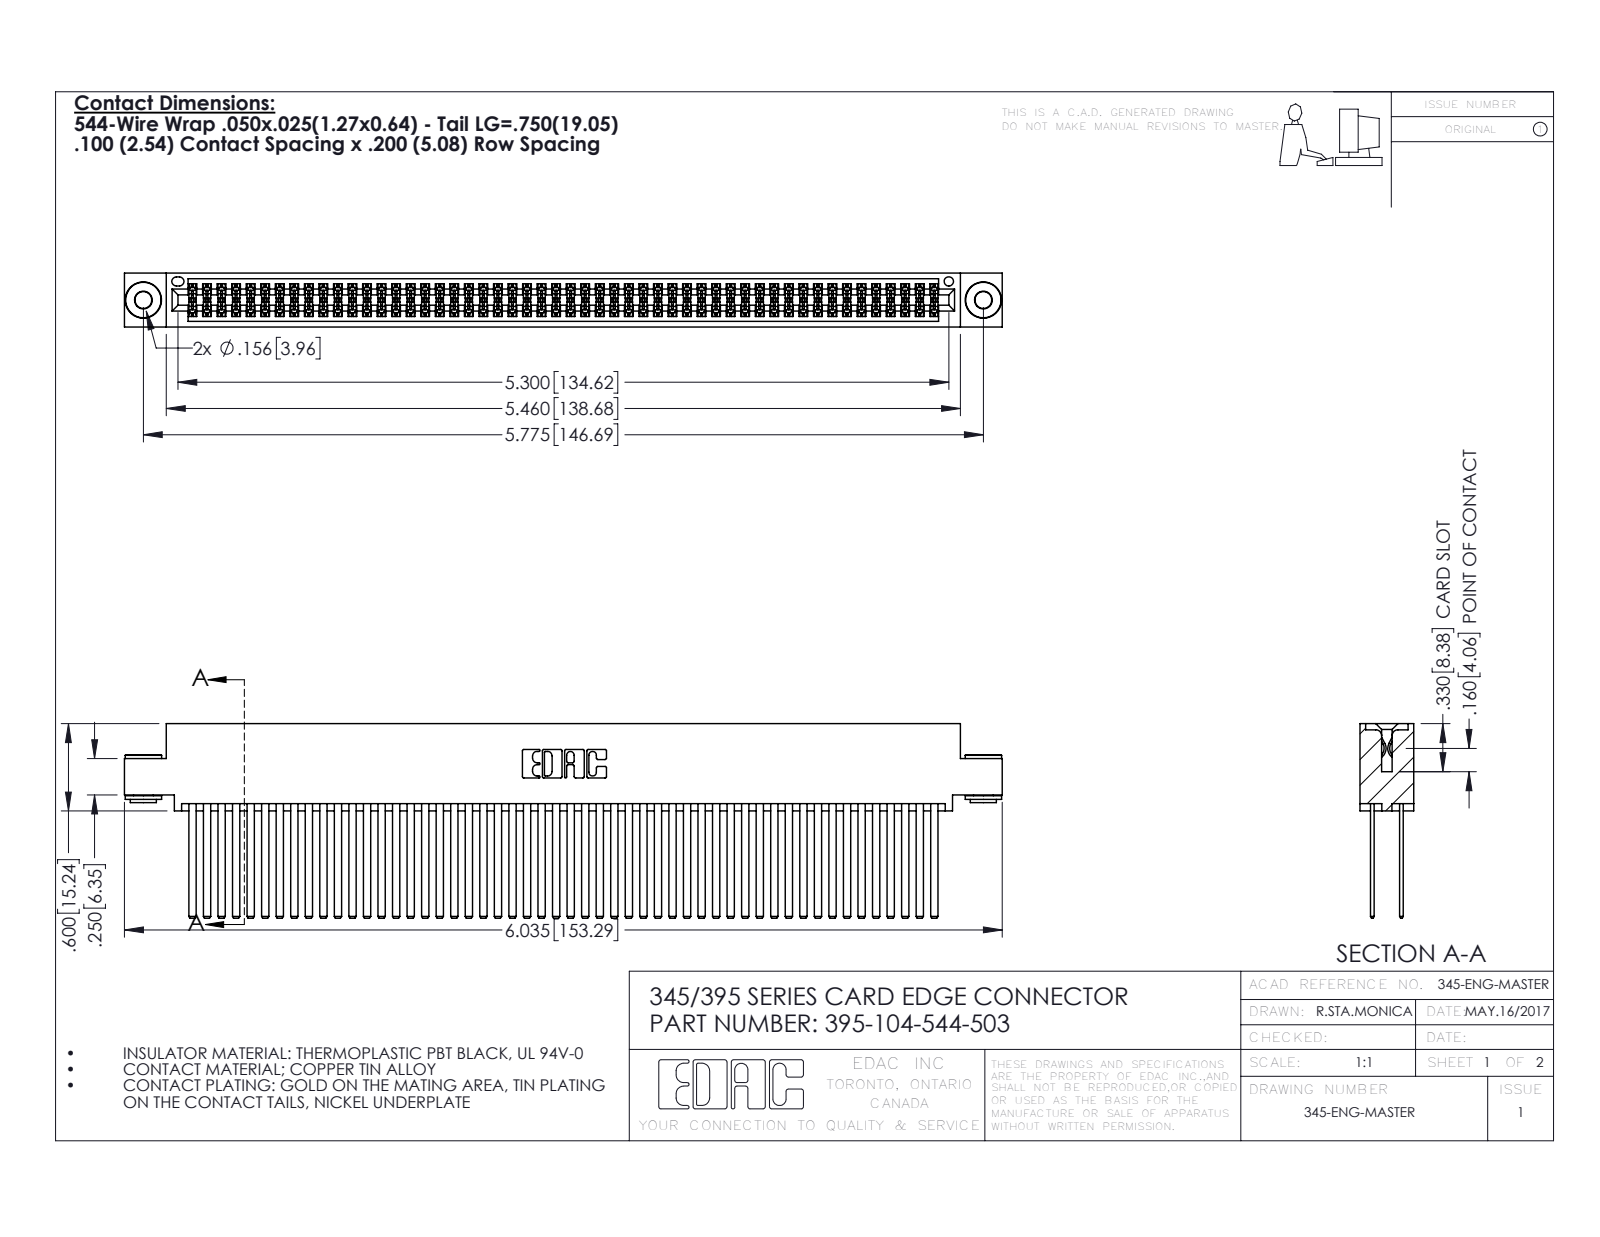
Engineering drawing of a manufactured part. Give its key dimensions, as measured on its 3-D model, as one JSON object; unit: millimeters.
{"part_name": "345-292-001_345-293-144; 345-250-002_345-250-002-102; 395-104-544-503; 345 Part_0.110 Offset - 0.156 Dia-TH", "step_written_by": "SolidWorks 2016 (CONFIG_CONTROL_DESIGN)", "units": "millimeters", "bodies": {"solids": 107, "faces": 4744, "planar": 3110, "cylindrical": 1626, "other": 8}, "overall_size": [153.3, 34, 9.4], "volume_mm3": 16390, "surface_area_mm2": 28990, "round_holes": [[2.9, 2], [4, 2], [1.6, 1]], "round_bosses_or_shafts": [[6.4, 2], [4.6, 2], [3.5, 2]], "partial_cylinders_radius": [[0.2, 156], [0.3, 22], [0.2, 6], [0.8, 6], [0.7, 3], [0.4, 2], [0.5, 2], [0.6, 2]], "face_to_face_distances": [5.1, 0.6, 1.8, 2.5, 6.9, 7.6, 5.7, 4.4, 9.4, 1.3], "hole_center_spacings": [6.9, 140.7, 146.7]}
